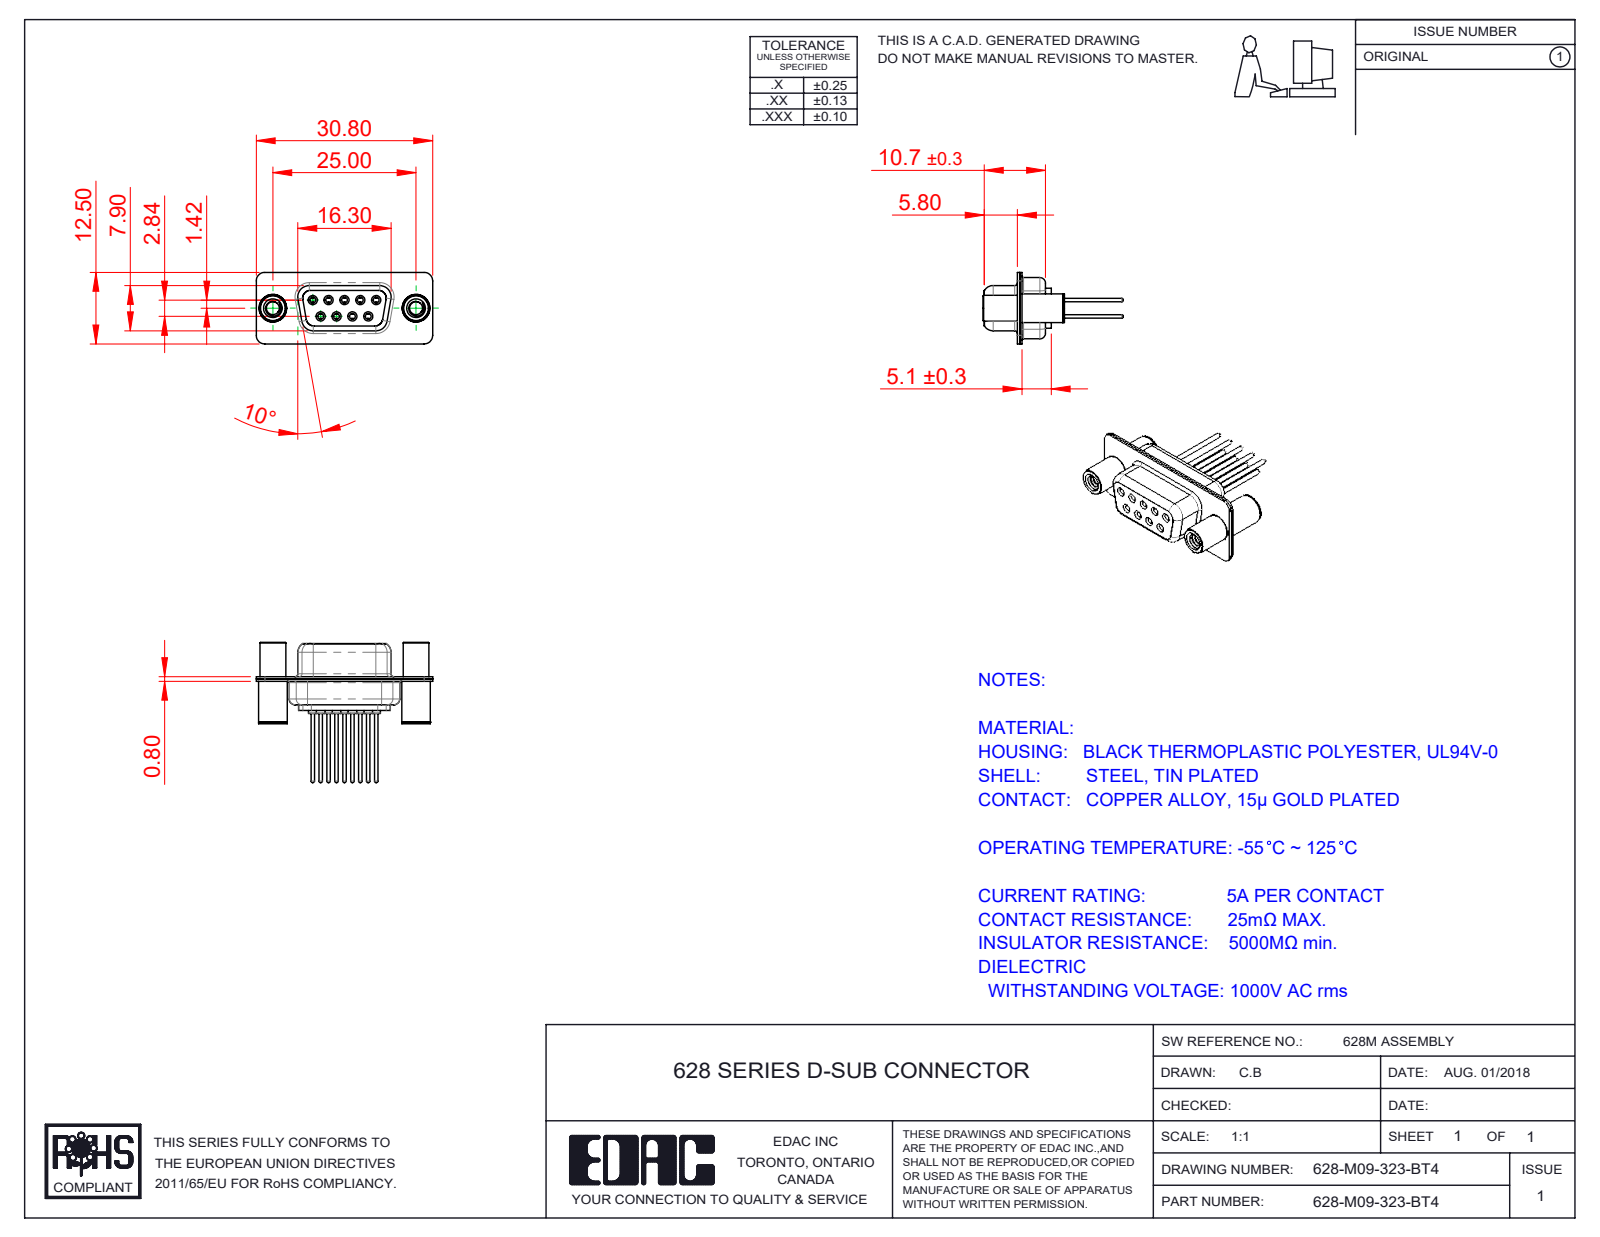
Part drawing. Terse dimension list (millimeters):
name: 628M Contact Row 1_23; 628M Shell Rear_09 Contacts; 628M Contact Row 2_23; 628M Housing_09 Contacts (+3 more)
written by: SolidWorks 2020 (CONFIG_CONTROL_DESIGN)
unit: mm
bodies: 14 solids, 860 faces (208 planar, 360 cylindrical, 292 other)
size: 30.8 × 24.47 × 12.5
volume: 2 006 mm³; area: 5 065 mm²
holes: 9× ⌀1, 9× ⌀1.1, 9× ⌀1.7, 9× ⌀1.8, 9× ⌀2, 2× ⌀2.26, 2× ⌀3.26, 2× ⌀4, 2× ⌀4.8
bosses: 9× ⌀2.2, 9× ⌀1.6, 9× ⌀1.5, 9× ⌀0.6, 2× ⌀5, 2× ⌀4.9, 2× ⌀4.5
rounds: 16× R1.5, 12× R2, 8× R1.35, 8× R1.6, 4× R0.25, 4× R0.5, 4× R0.6, 4× R0.65
face distances: 0.4, 1.4, 0.45, 8.45, 0.8, 1.8, 8.9, 1, 6.2, 7.05
hole spacings: 3.16, 2.77, 5.54, 5.03, 5.04, 8.31, 7.1, 7.48
